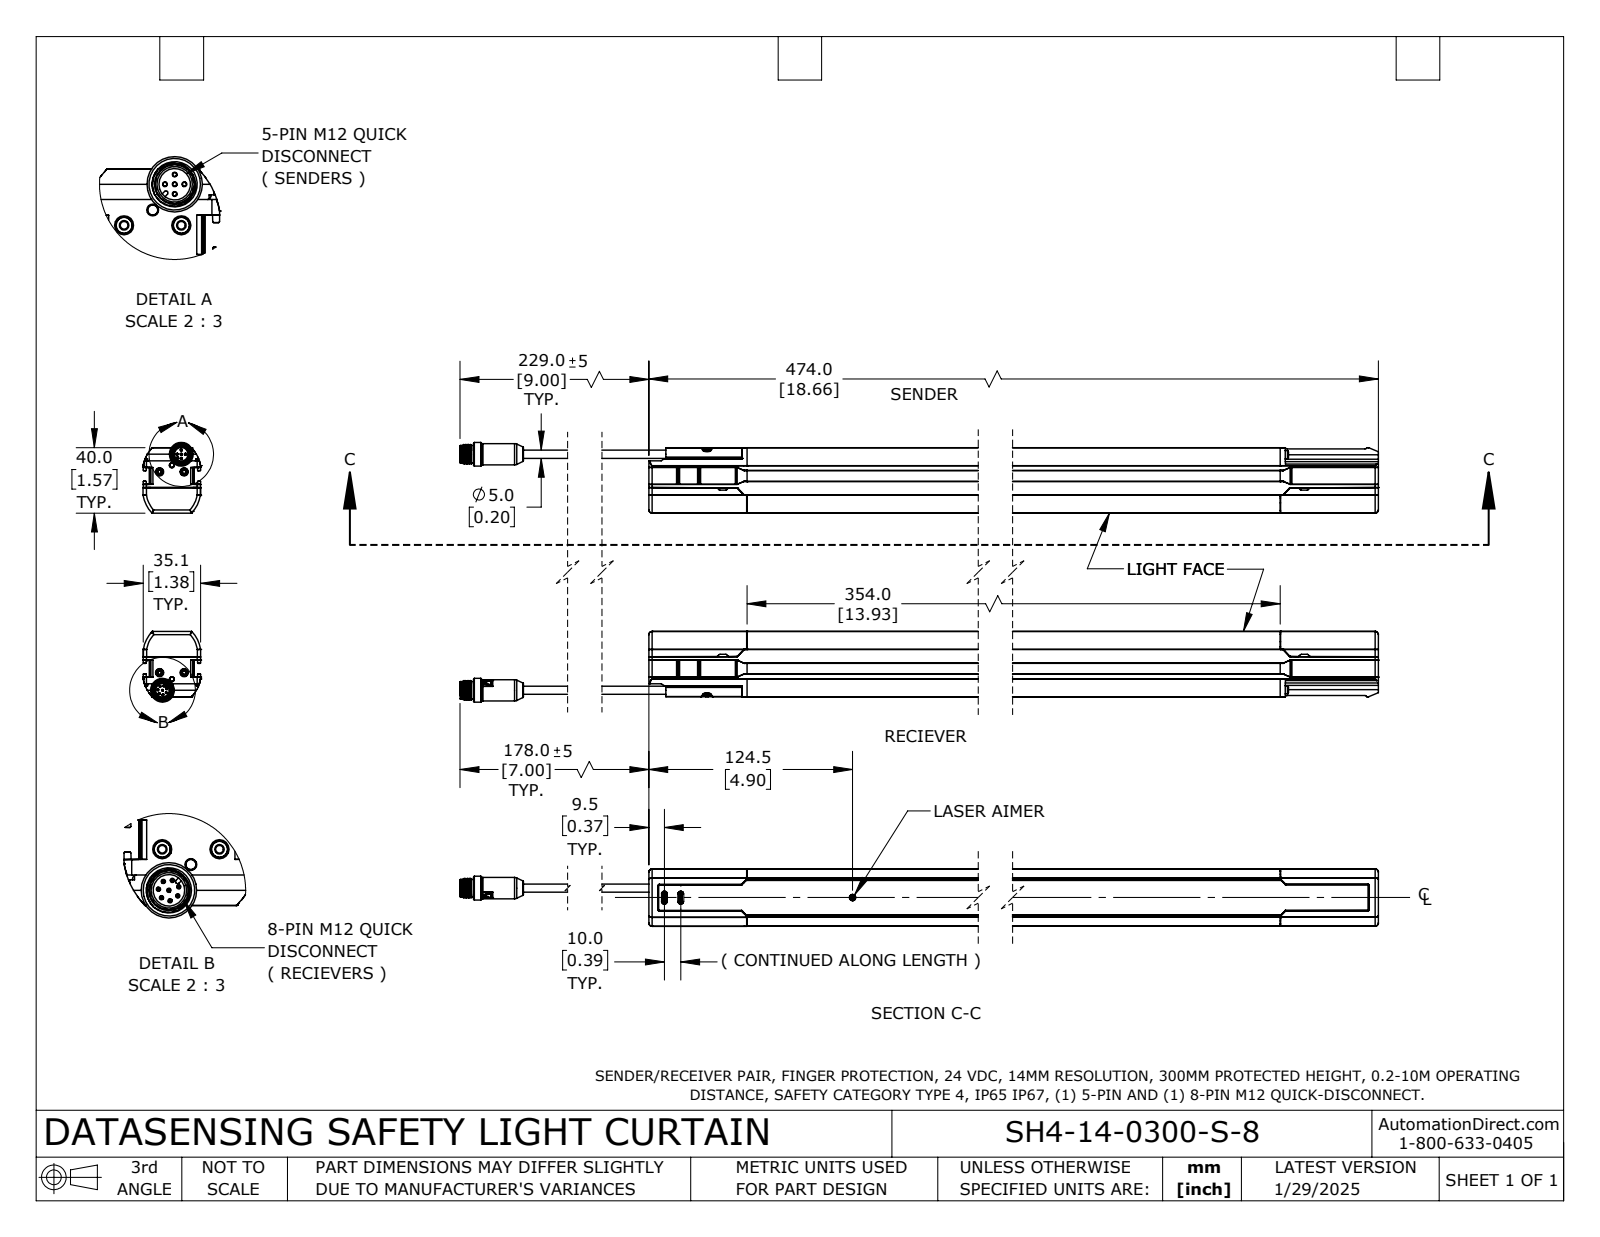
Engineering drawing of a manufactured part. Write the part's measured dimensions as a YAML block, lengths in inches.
part_name: "SH4-14-0300-S-8"
step_written_by: "SolidWorks 2024 (AUTOMOTIVE_DESIGN)"
units: inches
bodies: {solids: 5, faces: 2611, planar: 1187, cylindrical: 786, other: 638}
overall_size: [21.154, 6.212, 1.384]
volume: 42.64
surface_area: 264.4
round_holes:
  - {diameter: 0.079, count: 6}
  - {diameter: 0.118, count: 6}
  - {diameter: 0.197, count: 6}
  - {diameter: 0.101, count: 2}
  - {diameter: 0.102, count: 2}
  - {diameter: 0.102, count: 2}
  - {diameter: 0.103, count: 2}
  - {diameter: 0.138, count: 2}
  - {diameter: 0.325, count: 2}
  - {diameter: 0.382, count: 2}
  - {diameter: 0.407, count: 2}
  - {diameter: 0.425, count: 2}
round_bosses_or_shafts:
  - {diameter: 0.197, count: 11}
  - {diameter: 0.087, count: 8}
  - {diameter: 0.031, count: 8}
  - {diameter: 0.172, count: 6}
  - {diameter: 0.039, count: 5}
  - {diameter: 0.217, count: 4}
  - {diameter: 0.571, count: 2}
  - {diameter: 0.512, count: 2}
partial_cylinders:
  - {radius: 0.01, count: 174}
  - {radius: 0.016, count: 74}
  - {radius: 0.02, count: 50}
  - {radius: 0.008, count: 36}
  - {radius: 0.031, count: 26}
  - {radius: 0.047, count: 16}
  - {radius: 0.079, count: 14}
  - {radius: 0.031, count: 12}
face_to_face_distances: [1.496, 4.496, 3, 0.079, 1.033, 0.083, 1.417, 4.575, 3.079, 1.413]
hole_center_spacings: [0.591, 0.866, 0.433, 0.434, 0.019, 0.02, 0.245, 0.245]
